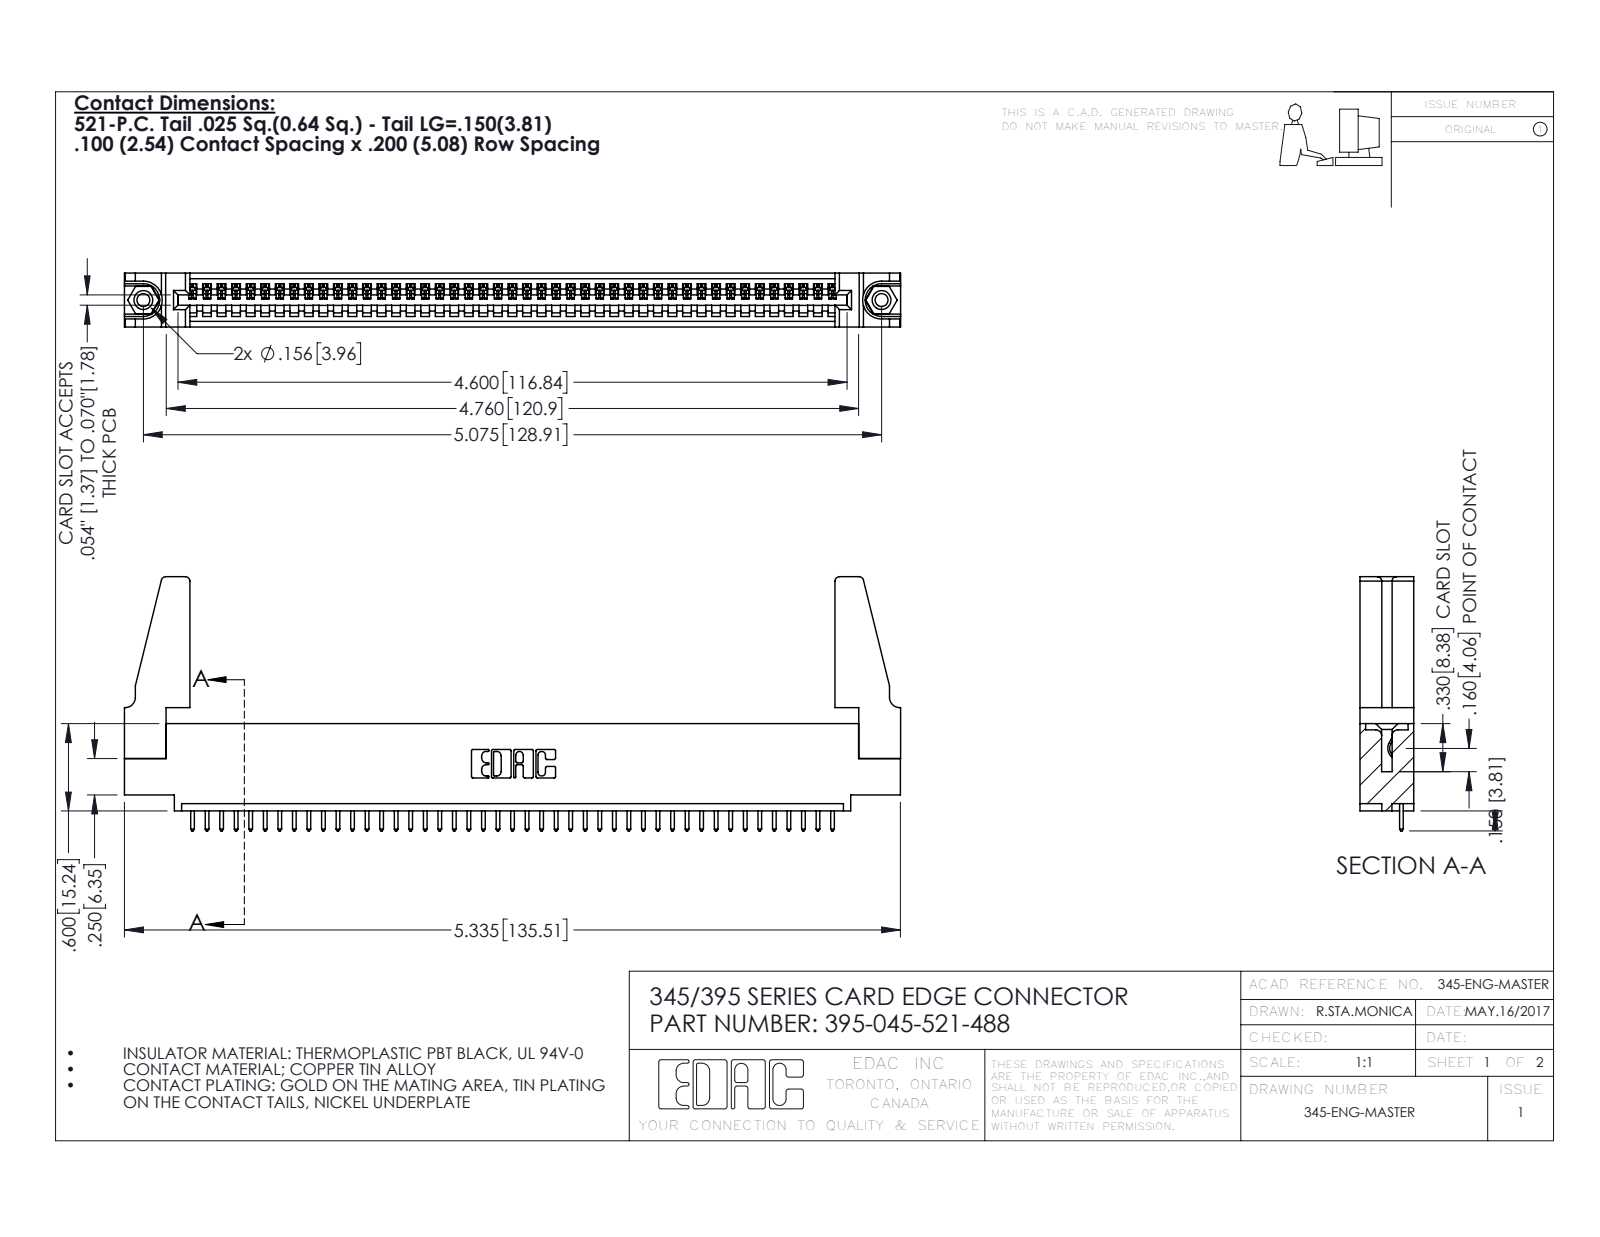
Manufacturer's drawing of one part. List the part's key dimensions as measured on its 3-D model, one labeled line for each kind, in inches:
Part name (STEP PRODUCT): 345 Part_0.110 Offset - 0.156 Dia-TH; 345-250-001_345-250-001-102; 345-220-078_345-220-088; 345-292-001_345-293-121 (+1 more)
STEP written by: SolidWorks 2016 (CONFIG_CONTROL_DESIGN)
Units: inches
Bodies: 50 solids, 2864 faces (1956 planar, 892 cylindrical, 16 other)
Overall size (bounding box): 5.336 × 1.747 × 0.37
Volume: 0.973 in³ · Surface area: 30.42 in²
Round holes (diameter × count): ⌀0.089 ×2, ⌀0.125 ×2, ⌀0.156 ×2, ⌀0.064 ×1
Round bosses / shafts (diameter × count): ⌀0.155 ×2
Partial cylindrical surfaces — rounded edges, fillets, slot ends (radius × count): R0.006 ×90, R0.01 ×90, R0.01 ×22, R0.03 ×8, R0.007 ×6, R0.031 ×6, R0.026 ×3, R0.031 ×2
Main face-to-face distances: 0.072, 0.298, 0.37, 0.2, 0.098, 0.272, 0.025, 0.225, 0.149, 0.072
Hole centre spacings: 0.27, 4.839, 5.075
